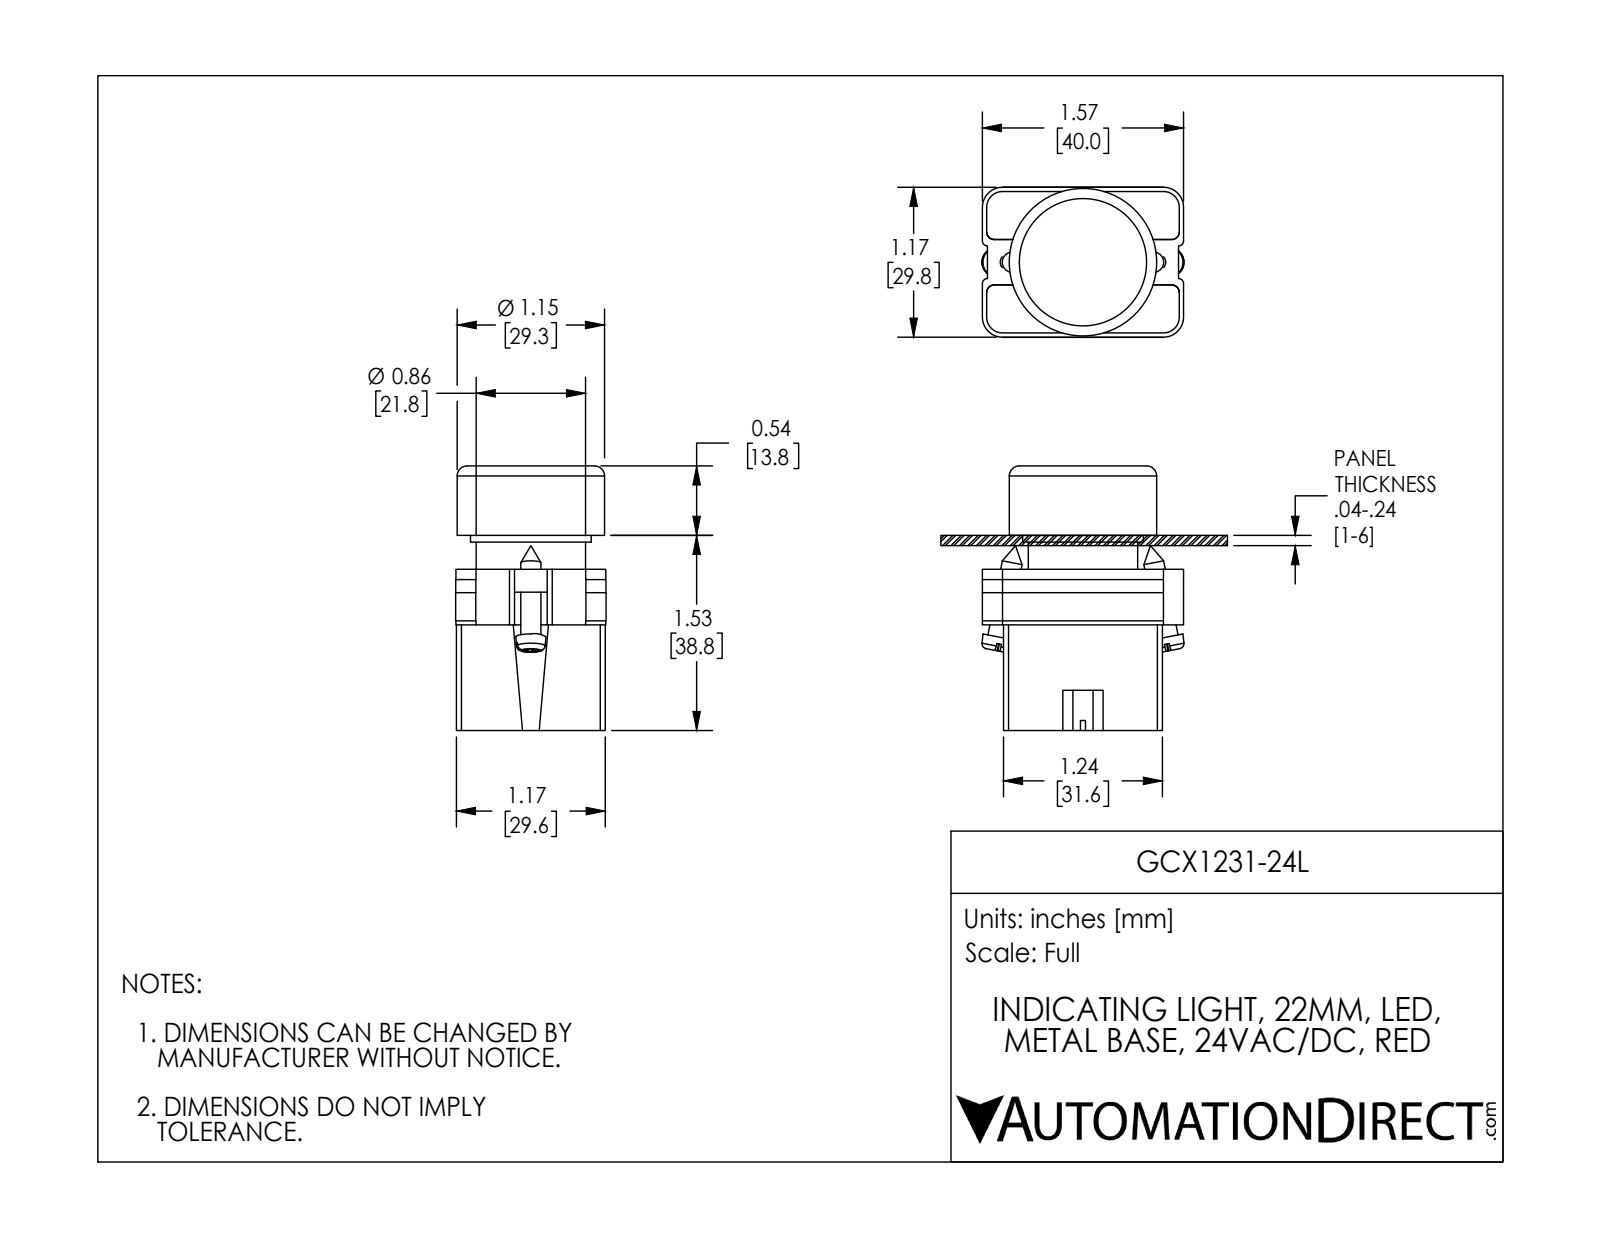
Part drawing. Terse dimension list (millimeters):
name: GCX1231-24L; GCX1231L OPERATOR; ecx1029; ECX1050
written by: SolidWorks 2016 (AUTOMOTIVE_DESIGN)
unit: mm
bodies: 7 solids, 339 faces (178 planar, 134 cylindrical, 27 other)
size: 52.6 × 40.2 × 29.9
volume: 37 170 mm³; area: 20 120 mm²
holes: 2× ⌀3.1, 2× ⌀3.3, 1× ⌀5, 1× ⌀11.9, 1× ⌀21.6, 1× ⌀22.3, 1× ⌀22.6, 1× ⌀28
bosses: 4× ⌀4, 1× ⌀29.3, 1× ⌀27.7, 1× ⌀24, 1× ⌀21.7, 1× ⌀19.8, 1× ⌀12.8
rounds: 24× R1.5, 12× R1, 12× R3.1, 12× R4, 8× R1, 2× R3.3, 1× R10, 1× R10.1
face distances: 21.8, 31.6, 21, 42.8, 28.9, 0.8, 49.9, 7, 0.8, 29.6
